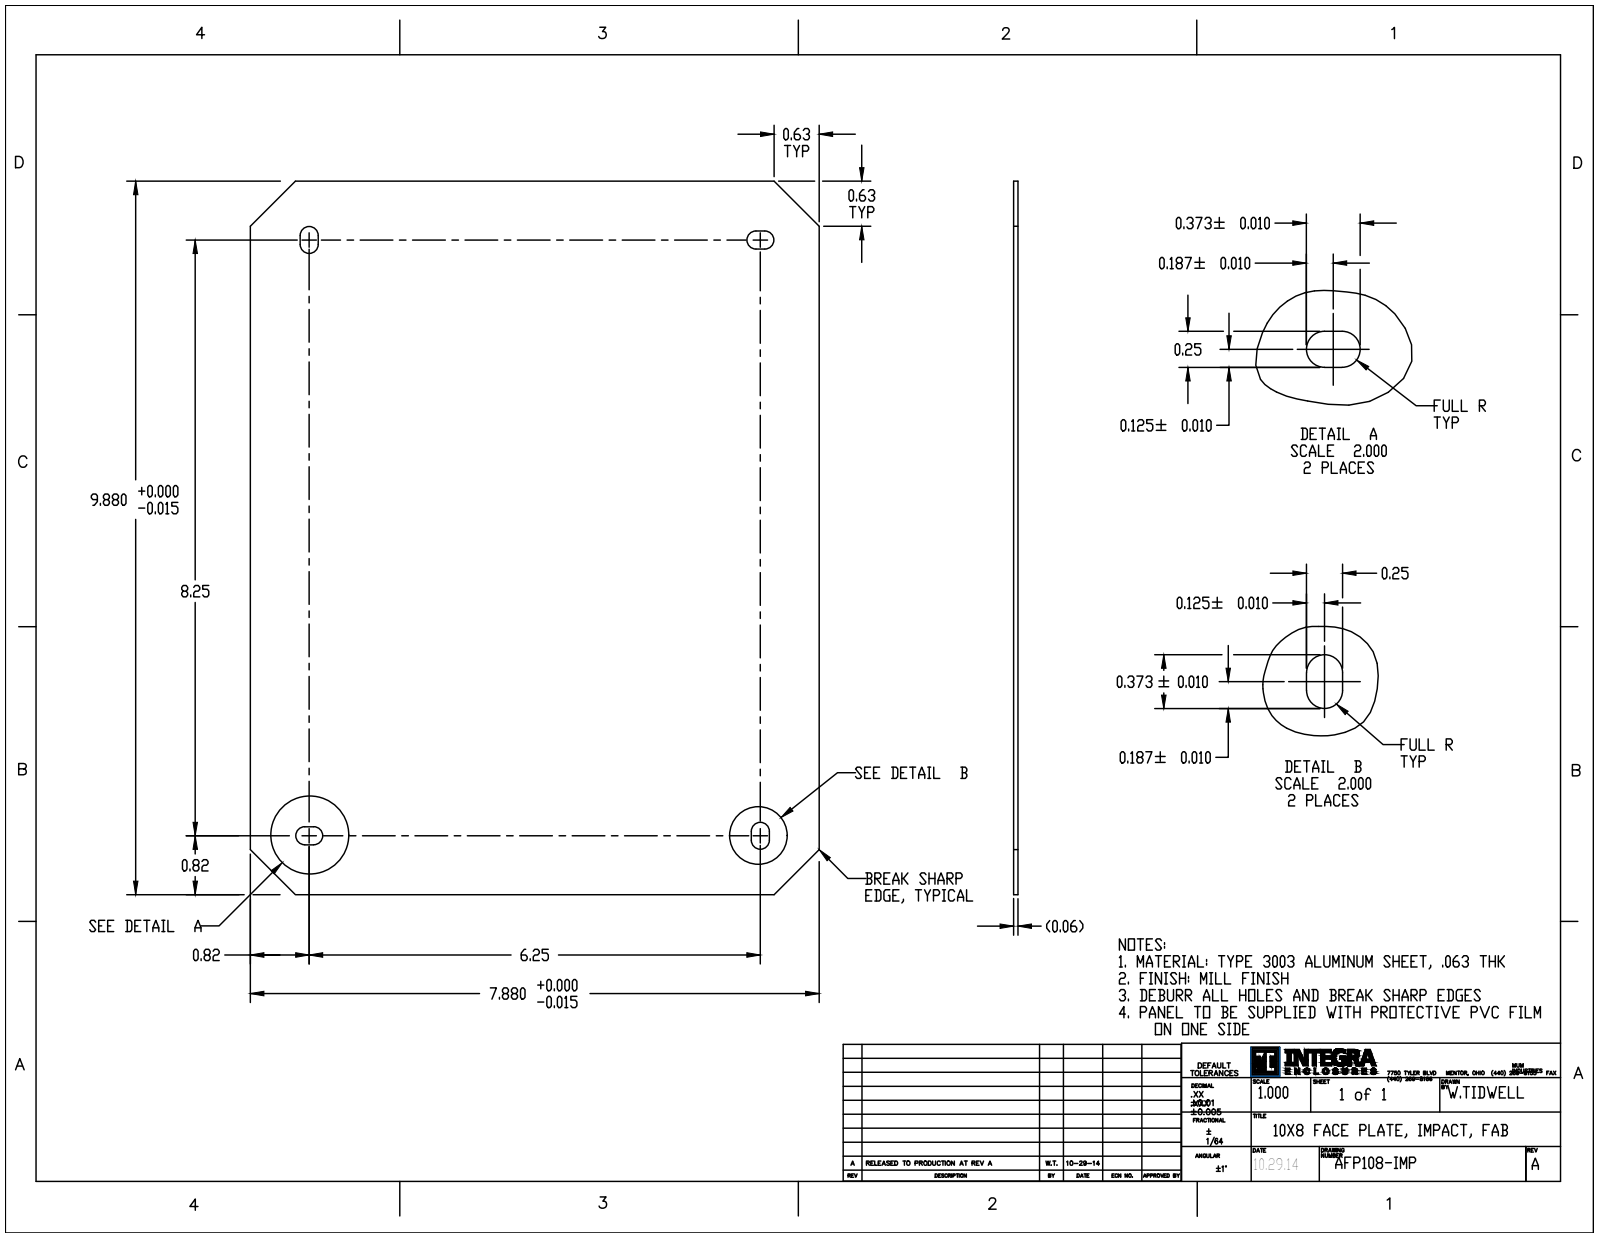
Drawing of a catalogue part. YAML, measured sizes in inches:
part_name: "AFP108-IMP; 9912511-20-50; 9912525-80-10; 9912511-20-50_ASM (+3 more)"
step_written_by: "CREO PARAMETRIC BY PTC INC, 2016050 (CONFIG_CONTROL_DESIGN)"
units: inches
bodies: {solids: 21, faces: 1746, planar: 378, cylindrical: 852, other: 516}
overall_size: [9.93, 7.93, 1.393]
volume: 7.216
surface_area: 195.9
round_holes:
  - {diameter: 0.19, count: 8}
  - {diameter: 0.246, count: 8}
  - {diameter: 0.357, count: 8}
  - {diameter: 0.25, count: 4}
round_bosses_or_shafts:
  - {diameter: 0.3, count: 8}
  - {diameter: 0.298, count: 8}
  - {diameter: 0.29, count: 8}
  - {diameter: 0.26, count: 8}
  - {diameter: 0.258, count: 8}
  - {diameter: 0.25, count: 8}
  - {diameter: 0.44, count: 4}
  - {diameter: 0.43, count: 4}
partial_cylinders:
  - {radius: 0.03, count: 112}
  - {radius: 0.004, count: 48}
  - {radius: 0.05, count: 32}
  - {radius: 0.005, count: 20}
  - {radius: 0.029, count: 16}
  - {radius: 0.046, count: 16}
  - {radius: 0.15, count: 12}
  - {radius: 0.02, count: 8}
face_to_face_distances: [0.063, 1.414, 6.121, 4.707, 1.2, 1.263, 6.215, 0.6, 4.801, 10.922]
hole_center_spacings: [8.25, 10.35, 6.25, 1.414, 6.25, 6.25, 10.35]
